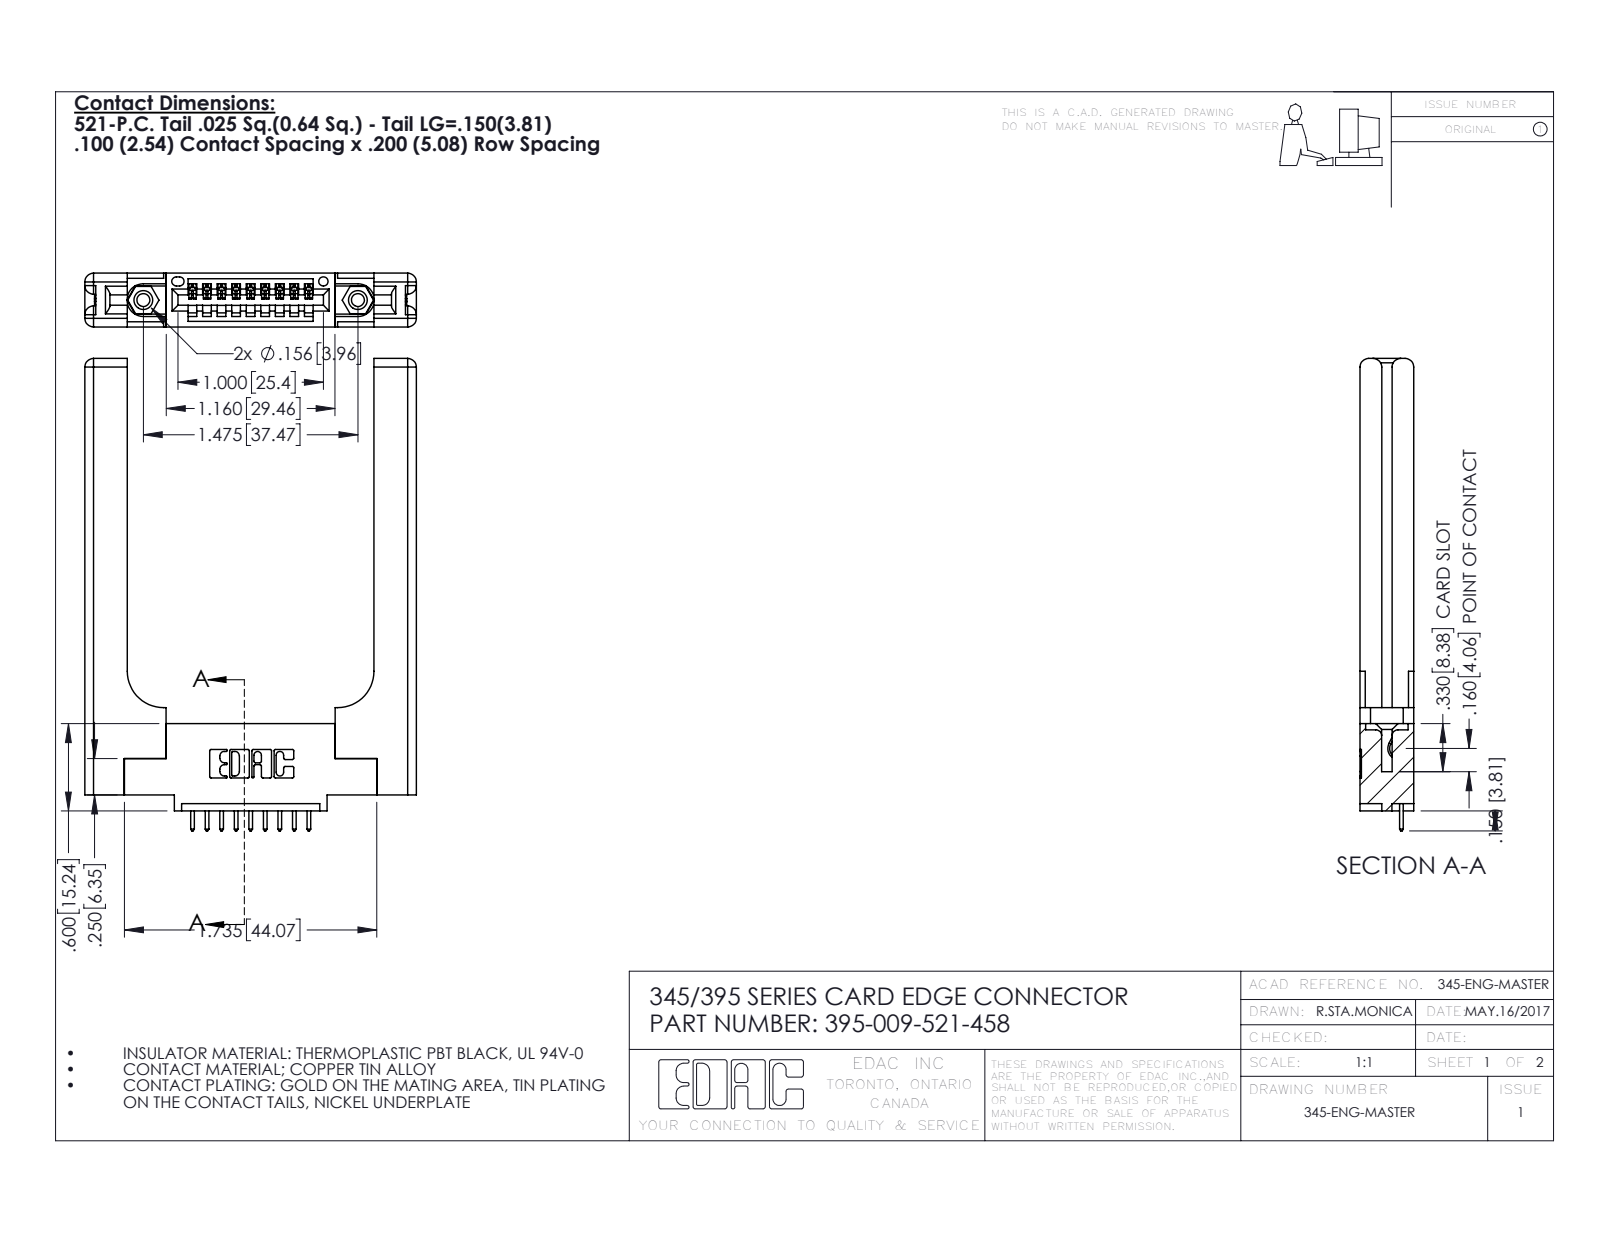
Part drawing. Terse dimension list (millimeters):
name: 345-220-058_345-220-058; 345-292-001_345-293-121; 345-250-001_345-250-001-102; 345 Part_0.110 Offset - 0.156 Dia-TH (+1 more)
written by: SolidWorks 2016 (CONFIG_CONTROL_DESIGN)
unit: mm
bodies: 14 solids, 908 faces (592 planar, 256 cylindrical, 60 other)
size: 82.5 × 57.9 × 9.4
volume: 13 600 mm³; area: 11 650 mm²
holes: 2× ⌀2.3, 2× ⌀3.2, 2× ⌀4, 1× ⌀1.6
bosses: 2× ⌀3.9
rounds: 22× R0.3, 18× R0.2, 18× R0.3, 16× R1.5, 6× R0.2, 6× R0.8, 3× R0.7, 2× R0.8
face distances: 9.4, 3.8, 5.6, 1.8, 2, 3.8, 7.6, 43.1, 1.8, 7.4
hole spacings: 6.9, 31.6, 37.5
